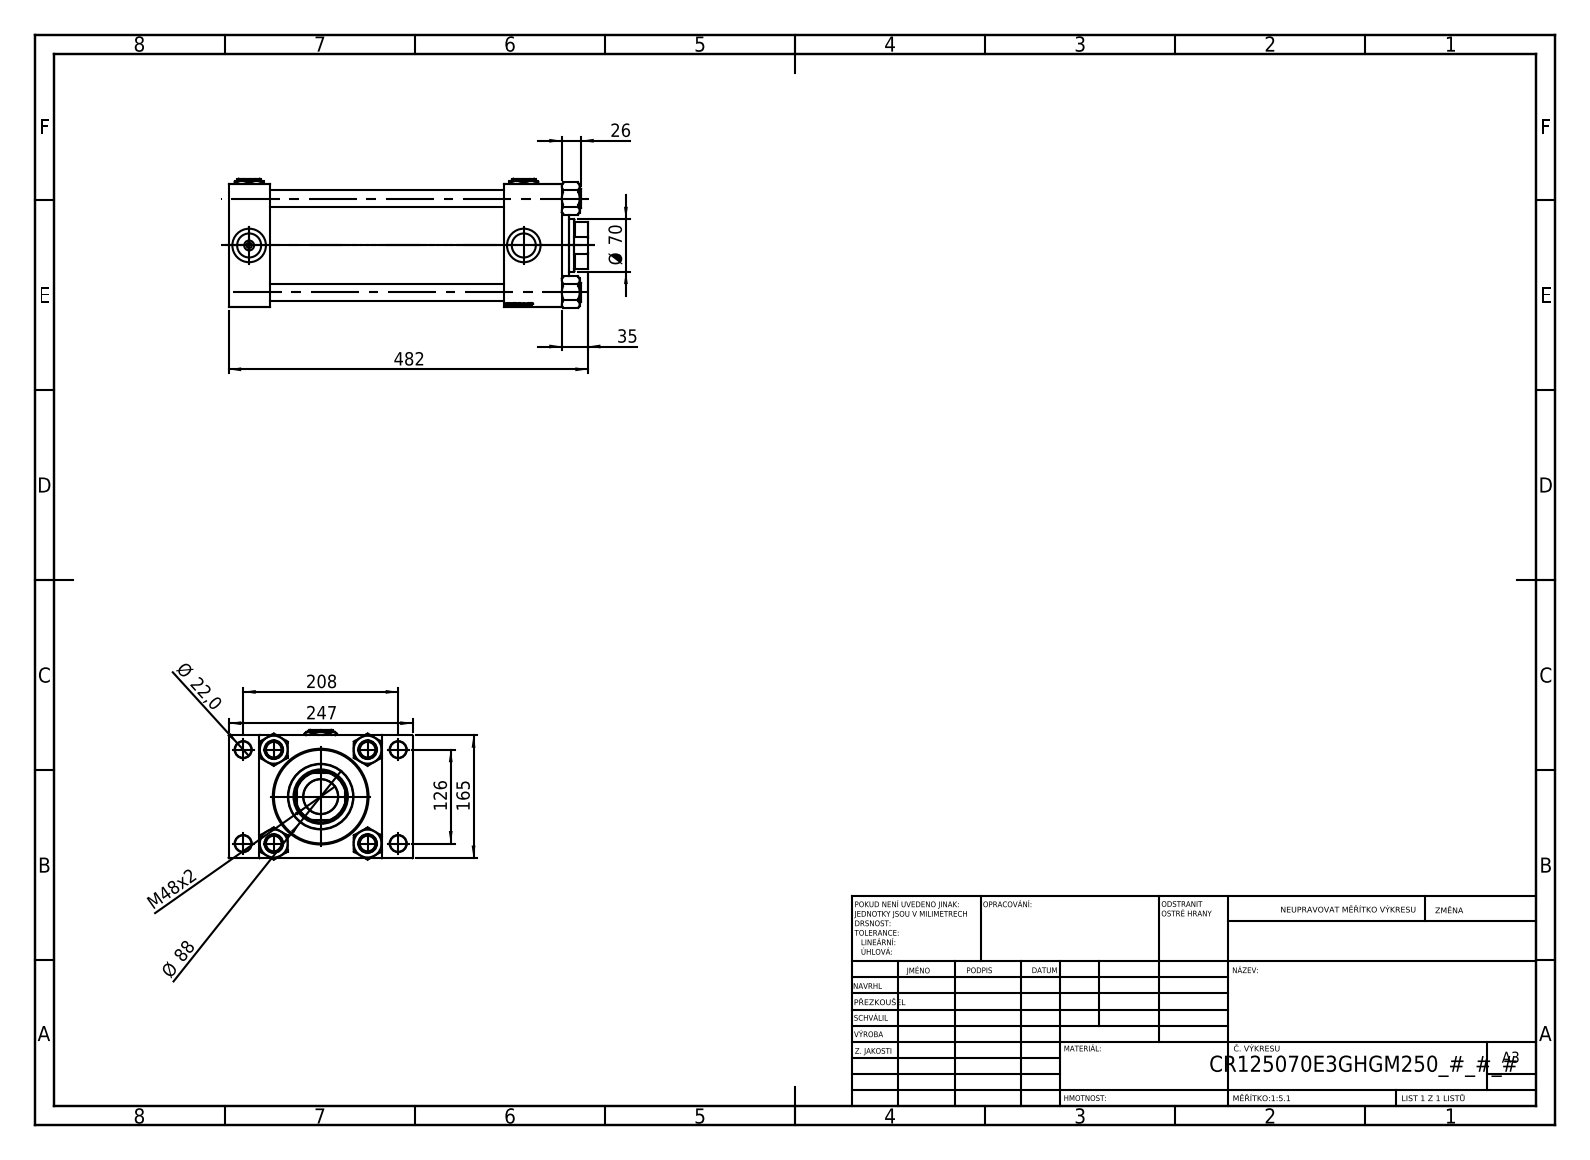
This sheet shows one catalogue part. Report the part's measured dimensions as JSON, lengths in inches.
{"part_name": "V215CR_E_Body; Zatka_pro_OIL_PORT; NUT_M5_E; V215_VC_A (+2 more)", "step_written_by": "SolidWorks 2019 (CONFIG_CONTROL_DESIGN)", "units": "inches", "bodies": {"solids": 13, "faces": 1284, "planar": 593, "cylindrical": 97, "other": 594}, "overall_size": [18.976, 9.724, 6.853], "volume_in3": 413.1, "surface_area_in2": 1380, "round_holes": [[0.866, 8], [1.269, 4], [1.772, 4], [0.276, 3], [1.831, 1], [2.756, 1], [2.874, 1], [3.78, 1], [4.921, 1], [4.941, 1]], "round_bosses_or_shafts": [[0.984, 4], [5.157, 1], [3.465, 1]], "partial_cylinders_radius": [[1.339, 1]], "face_to_face_distances": [2.165, 6.496, 17.598, 15.433, 1.614, 3.071, 14.528, 12.362, 8.11, 16.469], "hole_center_spacings": [1.616, 3.505, 4.787, 4.957, 5.215, 6.573, 8.233, 4.961]}
